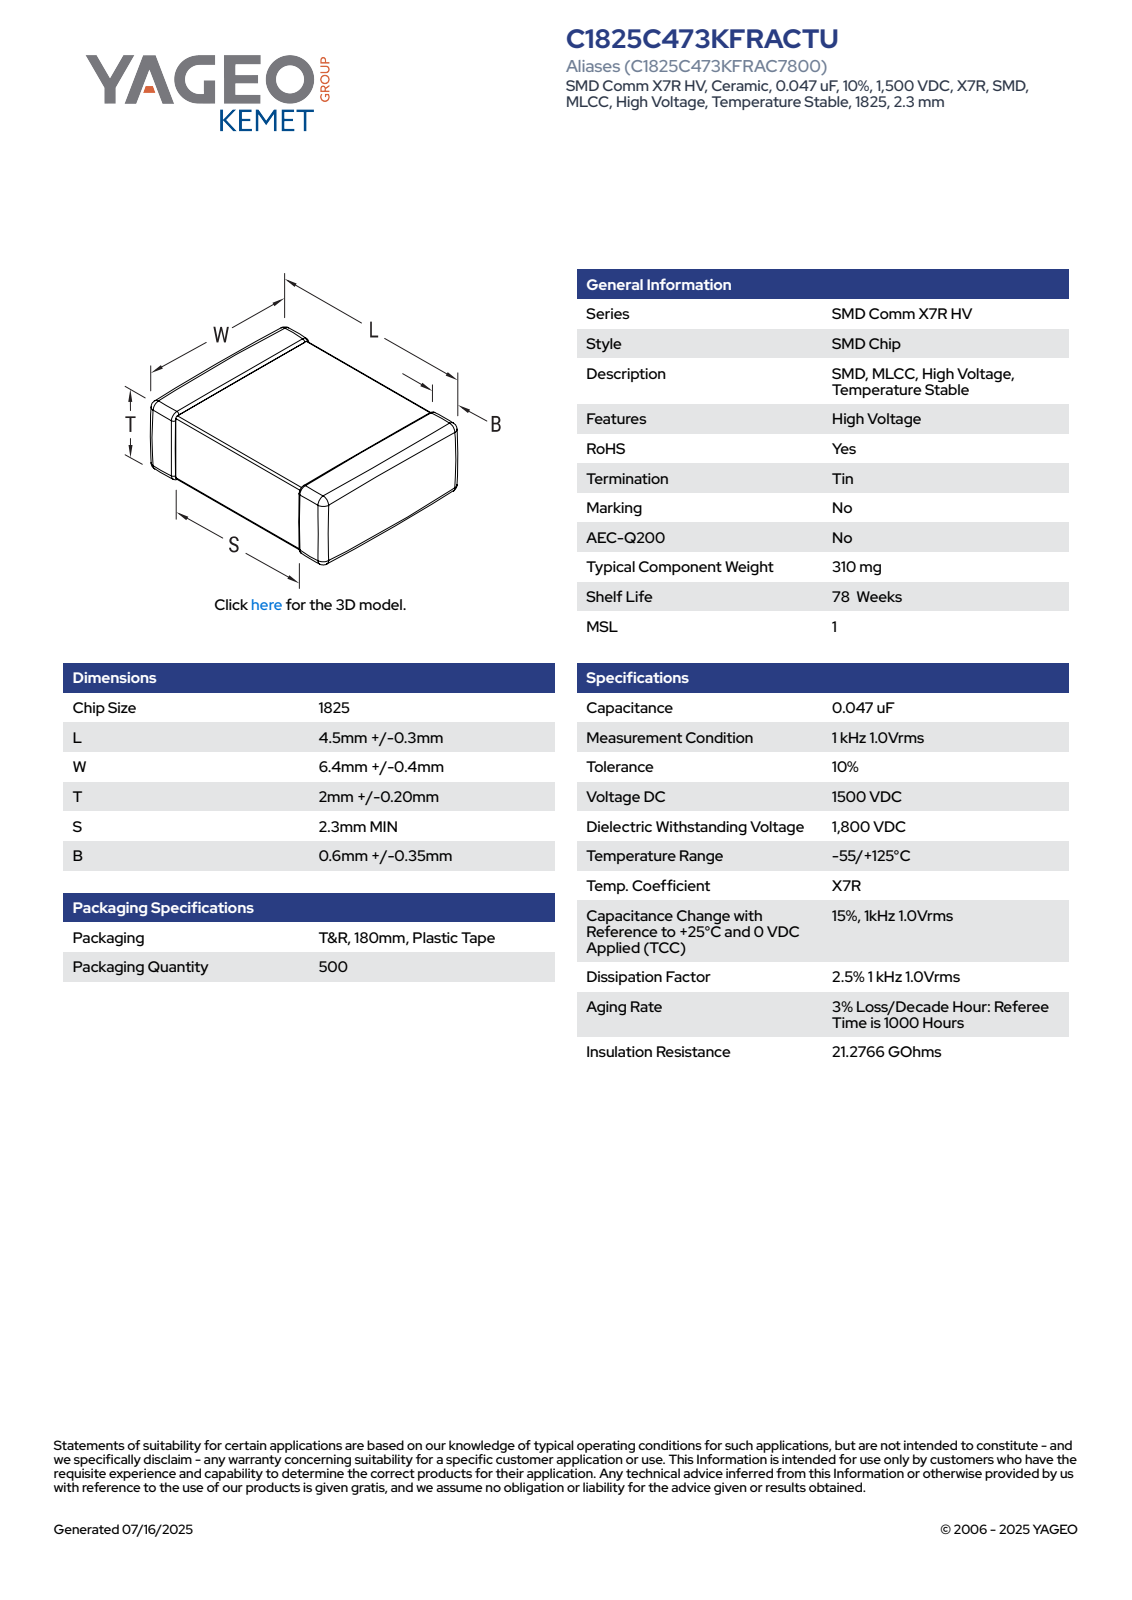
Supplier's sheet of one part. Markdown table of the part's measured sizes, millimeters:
| quantity | value |
| --- | --- |
| part name | CCS_CCSTDNOS_1825_L4.8W6.8T2.2B0.95 |
| STEP written by | SolidWorks 2014 (AUTOMOTIVE_DESIGN) |
| units | millimeters |
| bodies | 4 solids, 125 faces (71 planar, 38 cylindrical, 16 other) |
| overall size | 6.8 × 4.8 × 2.2 |
| volume | 64 mm³ |
| surface area | 113 mm² |
| partial cylindrical surfaces (radius × count) | 0.14 × 24 |
| main face-to-face distances | 1.92, 2.06, 4.8, 2.2, 6.66, 6.52, 6.8, 0.34, 3.56, 3.42 |
